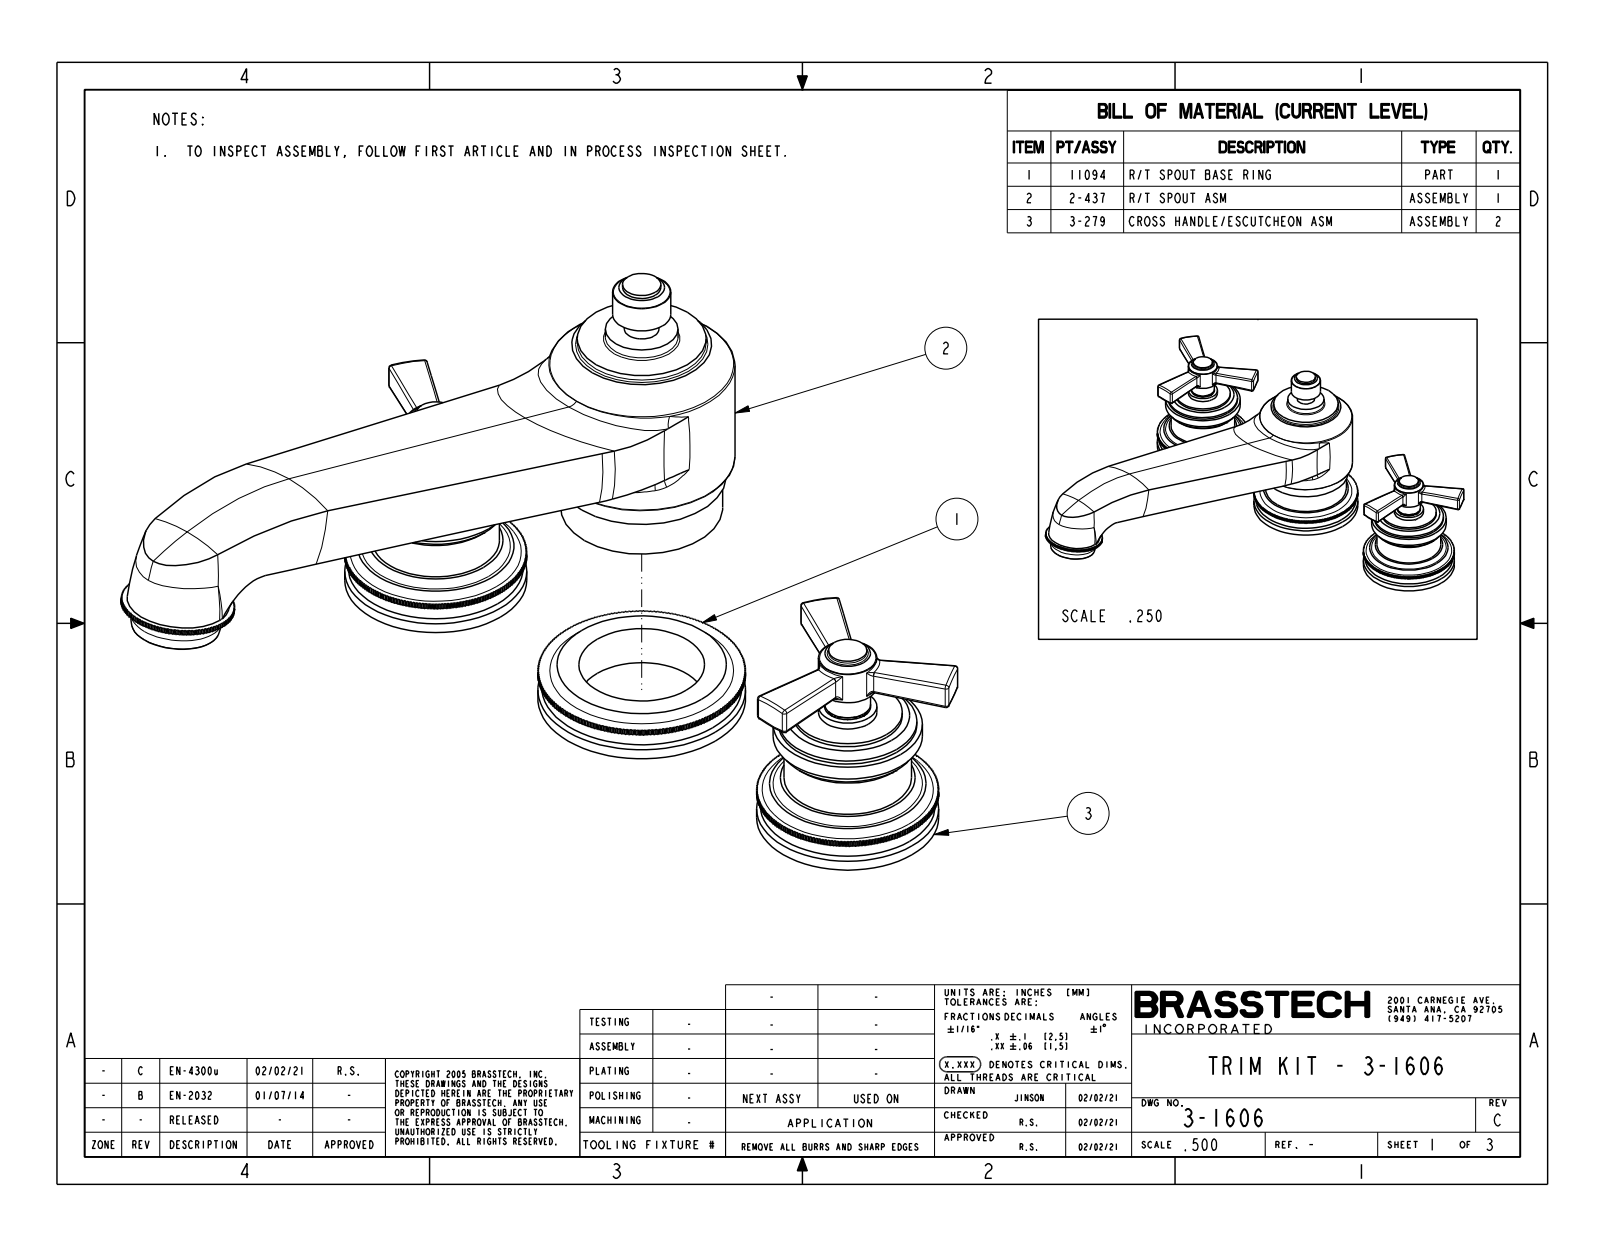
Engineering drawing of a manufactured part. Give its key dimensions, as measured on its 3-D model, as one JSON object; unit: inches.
{"part_name": "3-1606", "step_written_by": "CREO PARAMETRIC BY PTC INC, 2018400 (CONFIG_CONTROL_DESIGN)", "units": "inches", "bodies": {"solids": 3, "faces": 2322, "planar": 1343, "cylindrical": 732, "other": 247}, "overall_size": [11.211, 10.84, 4.645], "volume_in3": 46.26, "surface_area_in2": 150.7, "round_bosses_or_shafts": [[0.8, 3], [0.525, 3], [2.5, 2], [2.4, 2], [2.05, 2], [1.9, 2], [1.75, 2], [1.5, 2]], "partial_cylinders_radius": [[0.04, 12], [0.1, 12], [0.781, 1]], "face_to_face_distances": [1.3, 1.775, 0.2, 0.475, 0.4, 0.1, 1.375, 0.15, 3.42, 2.945]}
